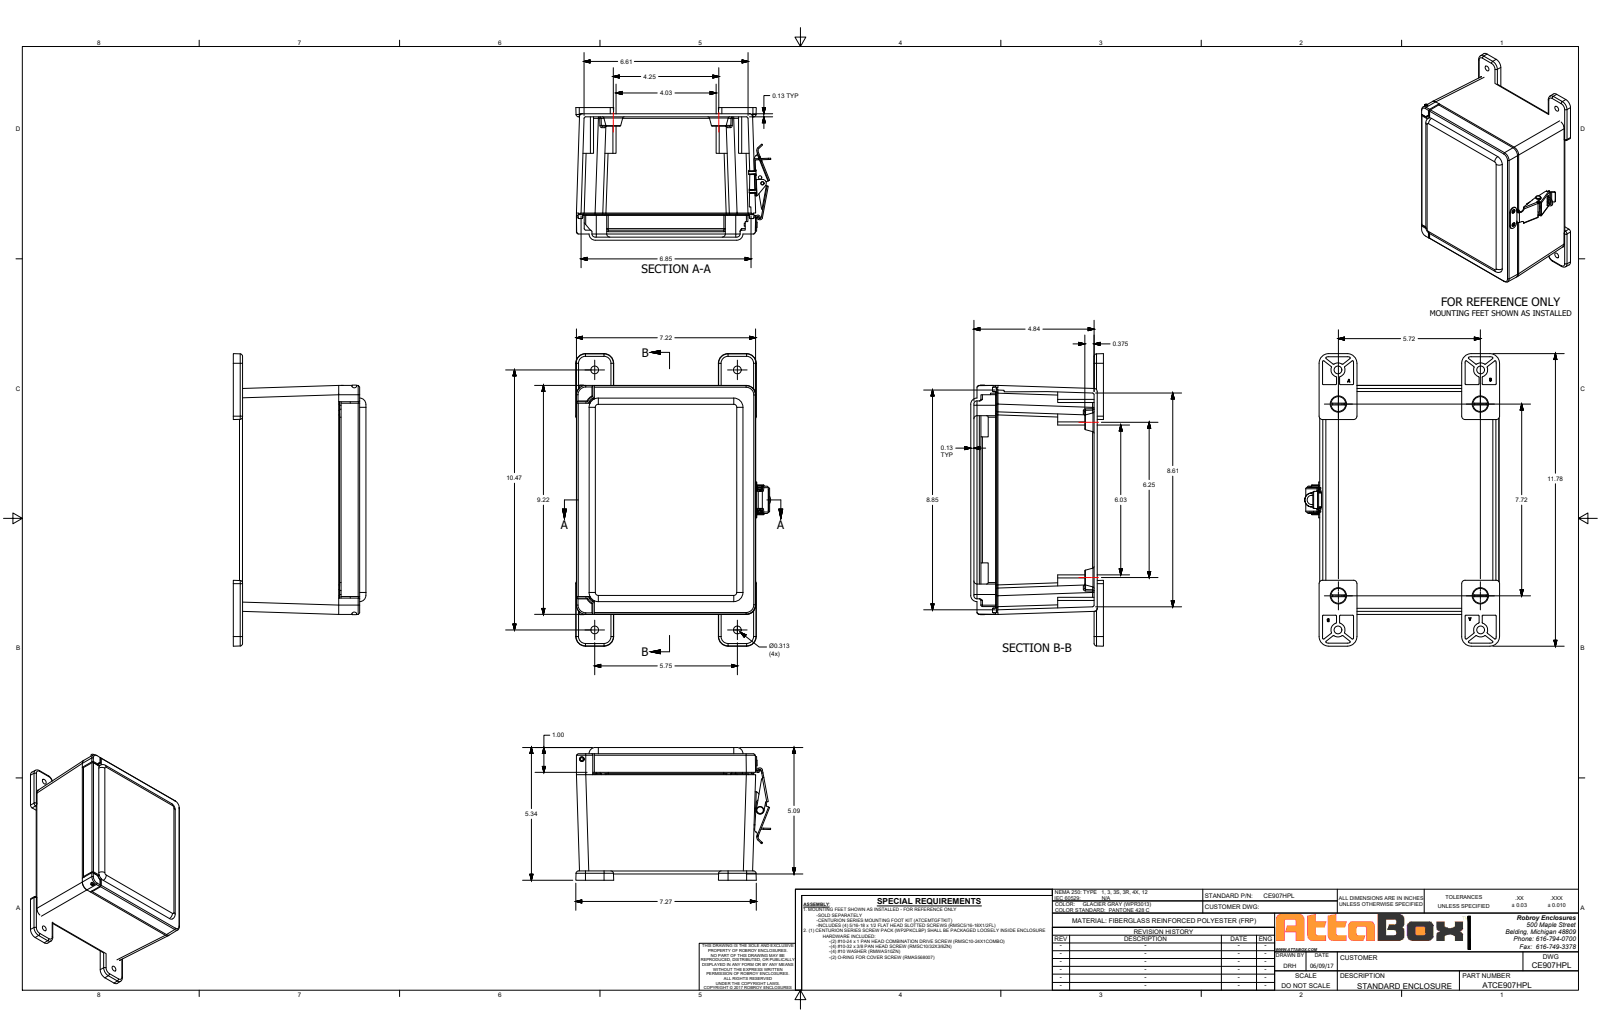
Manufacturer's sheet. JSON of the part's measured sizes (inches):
{"part_name": "CE907HPL", "step_written_by": "SolidWorks 2018 (AUTOMOTIVE_DESIGN)", "units": "inches", "bodies": {"solids": 36, "faces": 1587, "planar": 689, "cylindrical": 497, "other": 401}, "overall_size": [11.783, 7.85, 5.344], "volume_in3": 61.96, "surface_area_in2": 717.4, "round_holes": [[0.159, 6], [0.281, 6], [0.14, 4], [0.156, 4], [0.313, 4], [0.313, 4], [0.344, 4], [0.531, 4], [0.075, 2], [0.096, 2], [0.104, 2], [0.13, 2]], "round_bosses_or_shafts": [[0.27, 6], [0.229, 4], [0.125, 4], [0.375, 2], [0.325, 1], [0.325, 1], [0.3, 1], [0.299, 1]], "partial_cylinders_radius": [[0.031, 58], [0.031, 56], [0.125, 42], [0.062, 19], [0.25, 16], [0.1, 12], [0.063, 11], [0.375, 10]], "face_to_face_distances": [0.125, 4.969, 0.186, 5.094, 4.844, 0.25, 0.125, 0.186, 5.219, 0.75], "hole_center_spacings": [10.177, 0.75, 2.238, 5.04, 5.426, 5.511, 5.896, 6.14]}
